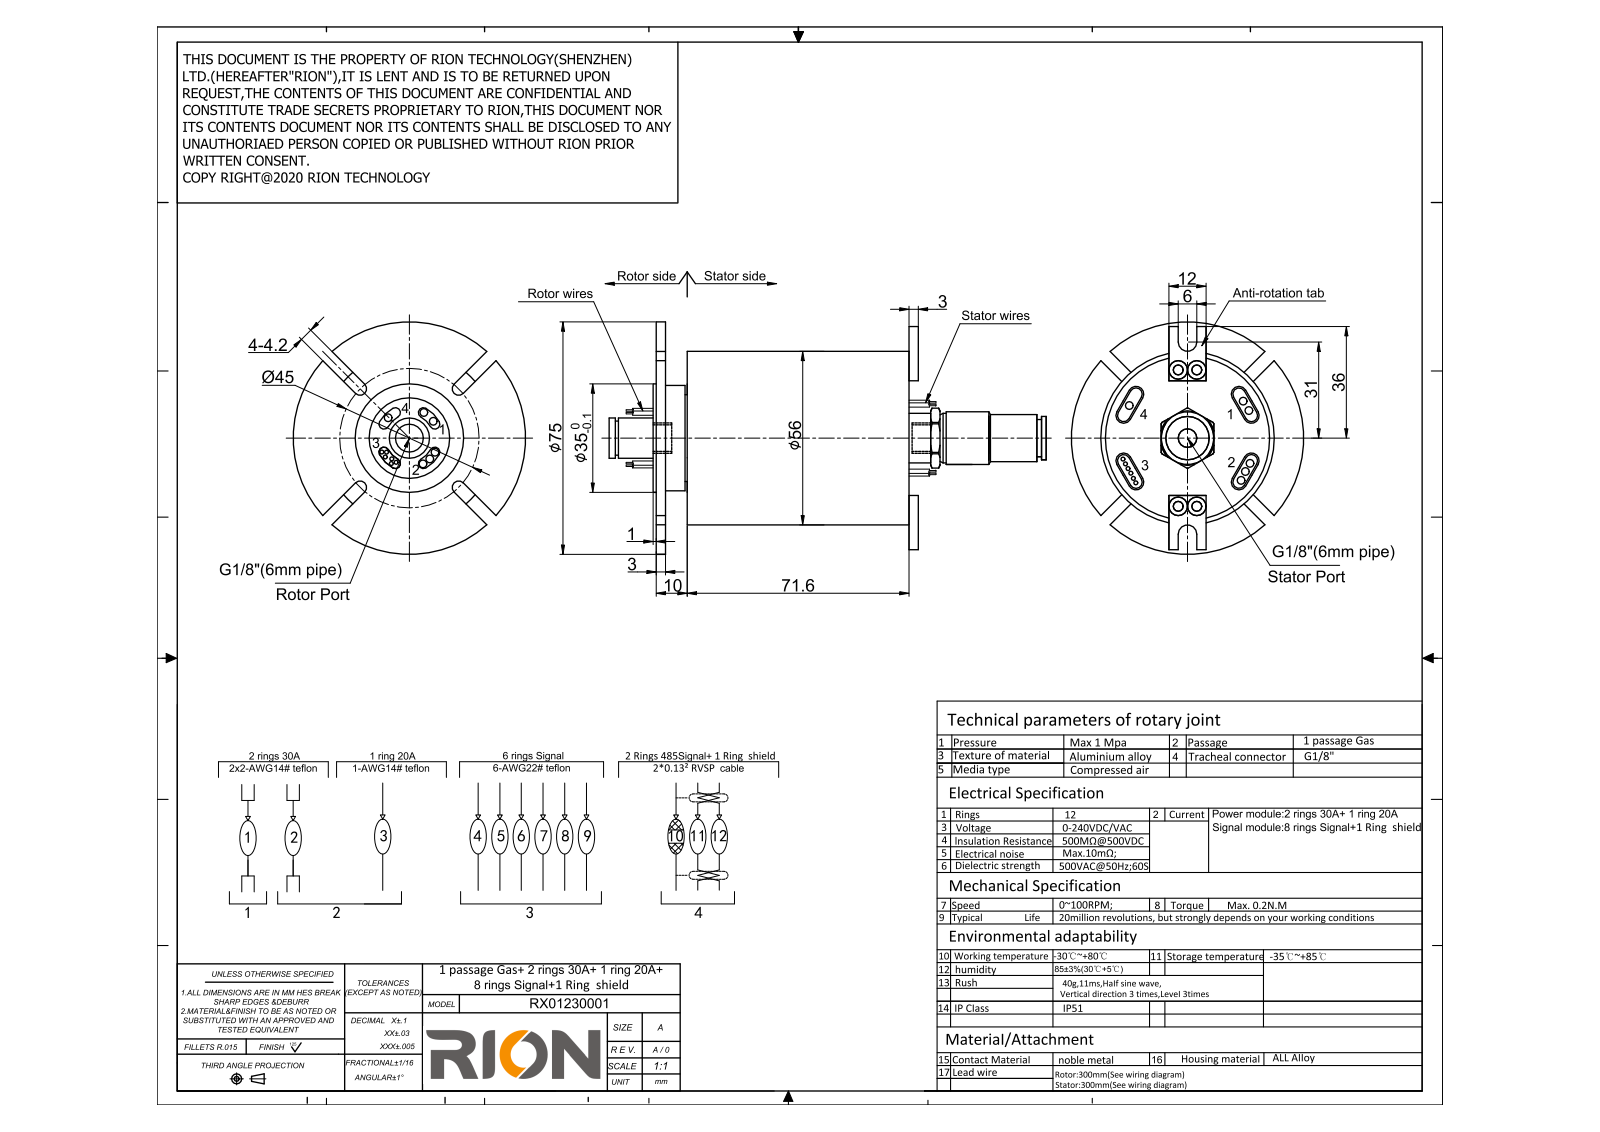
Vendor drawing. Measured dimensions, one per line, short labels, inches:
name: KSH06-01S; KQ2S06-01S
written by: SolidWorks 2014 (CONFIG_CONTROL_DESIGN)
unit: in
bodies: 3 solids, 352 faces (132 planar, 180 cylindrical, 40 other)
size: 5.051 × 2.953 × 2.953
volume: 12.03 in³; area: 58.88 in²
holes: 5× ⌀0.236, 4× ⌀0.098, 4× ⌀0.126, 1× ⌀0.157, 1× ⌀0.276, 1× ⌀0.346, 1× ⌀0.5, 1× ⌀0.677, 1× ⌀1.024, 1× ⌀2.087
bosses: 12× ⌀0.098, 12× ⌀0.051, 1× ⌀2.953, 1× ⌀2.205, 1× ⌀2.079, 1× ⌀1.378, 1× ⌀1.339, 1× ⌀1.102
rounds: 8× R0.064, 8× R0.079, 4× R0.083, 2× R0.118, 1× R0.305, 1× R0.433
face distances: 0.118, 3.213, 3.094, 0.394, 0.276, 2.819, 0.157, 0.433, 3.252, 0.039
hole spacings: 0.396, 0.617, 0.835, 0.874, 1.595, 1.663, 0.236, 0.945
